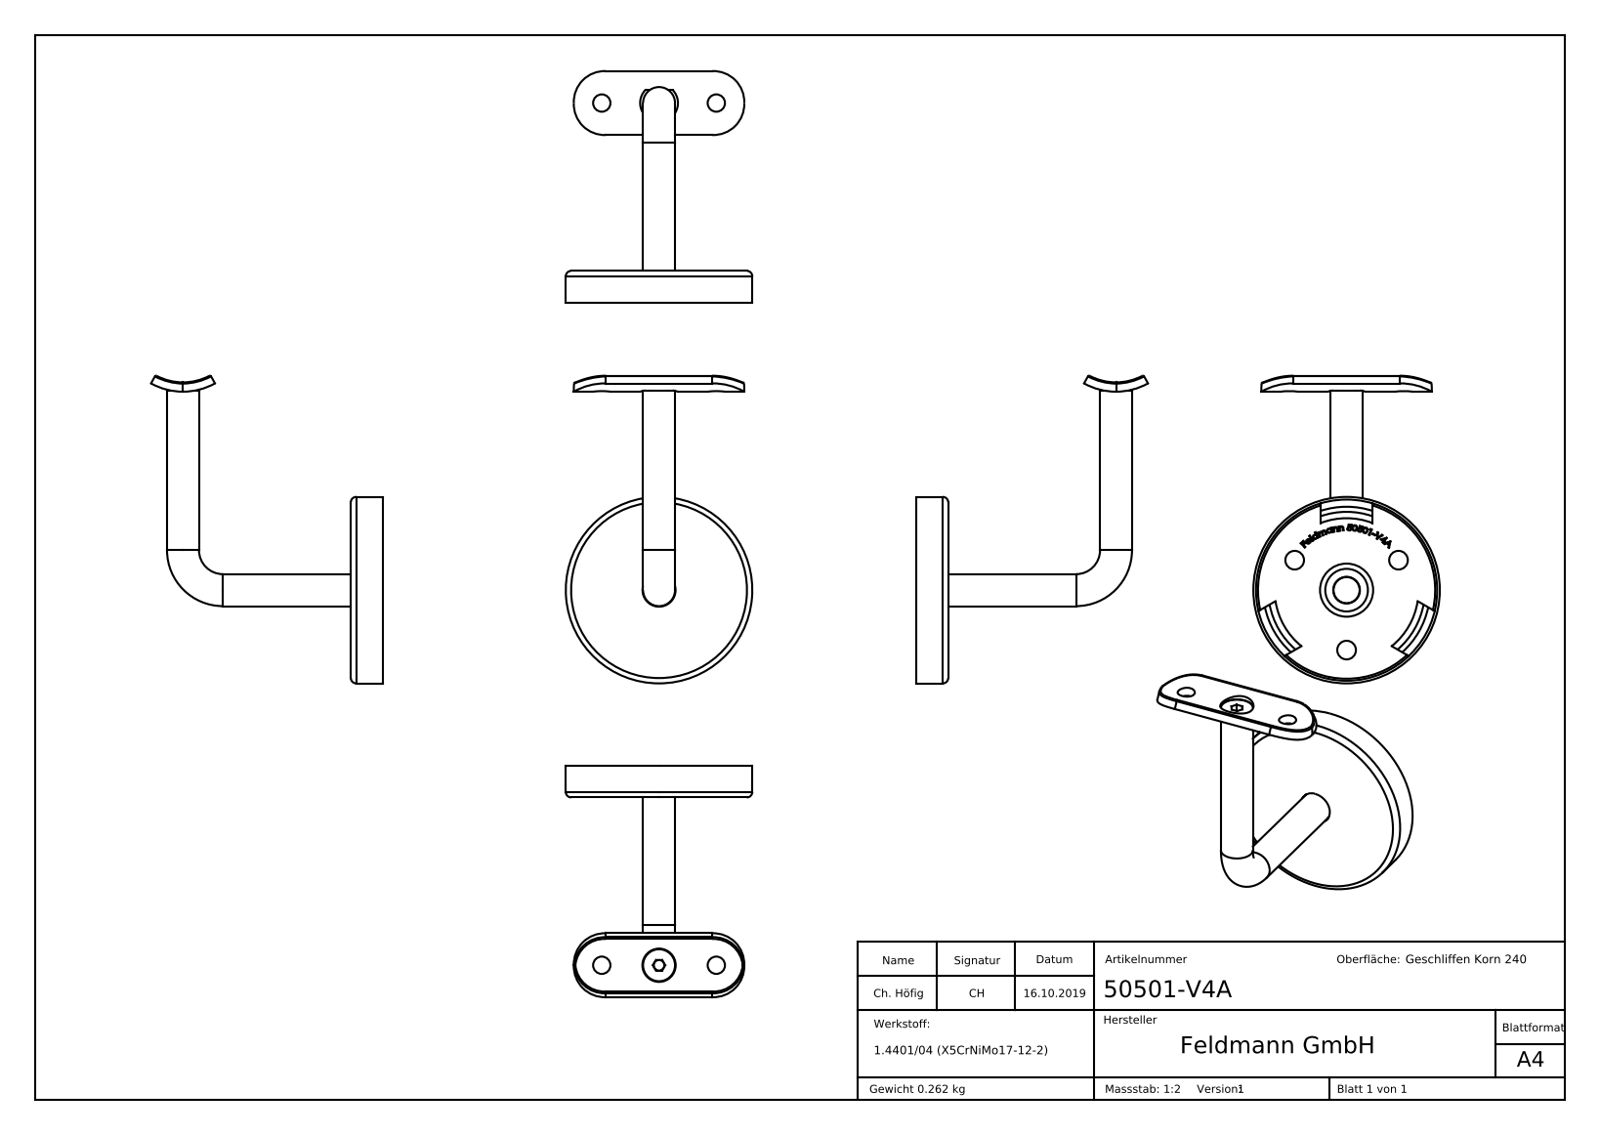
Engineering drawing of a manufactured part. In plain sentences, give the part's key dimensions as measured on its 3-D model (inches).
The part is named "60182-240; 5050X-240 Teil3_5050X-V4A-AR; 5050X-240 Teil1; 5050X-240 Teil1_50500-240-P (+7 more)". Its 3-D file was written by "SolidWorks 2015 (CONFIG_CONTROL_DESIGN)". It is 5 solids with 329 faces: 175 planar, 40 cylindrical and 114 other. Overall it measures 4.547 by 3.425 by 2.756 inches. Its volume is 2.004 cubic inches and its surface area 45.72 square inches. Round holes: 3 of diameter 0.276, 2 of diameter 0.256, 1 of diameter 0.197, 1 of diameter 0.323, 1 of diameter 0.394, 1 of diameter 0.488, 1 of diameter 0.492. Round bosses or shafts: 2 of diameter 0.472, 1 of diameter 2.756, 1 of diameter 2.677, 1 of diameter 0.386, 1 of diameter 0.236. Partial cylindrical surfaces (rounded edges, fillets, slot ends): 4 of radius 0.472, 2 of radius 0.02, 1 of radius 0.28, 1 of radius 0.835, 1 of radius 0.972, 1 of radius 1.309. The main face-to-face distances are 0.039, 0.472, 0.433, 0.079, 0.354, 0.394, 0.126, 0.047, 0.205, 0.228. The hole center spacings are 0.886, 0.846, 1.534, 1.535, 1.693.
